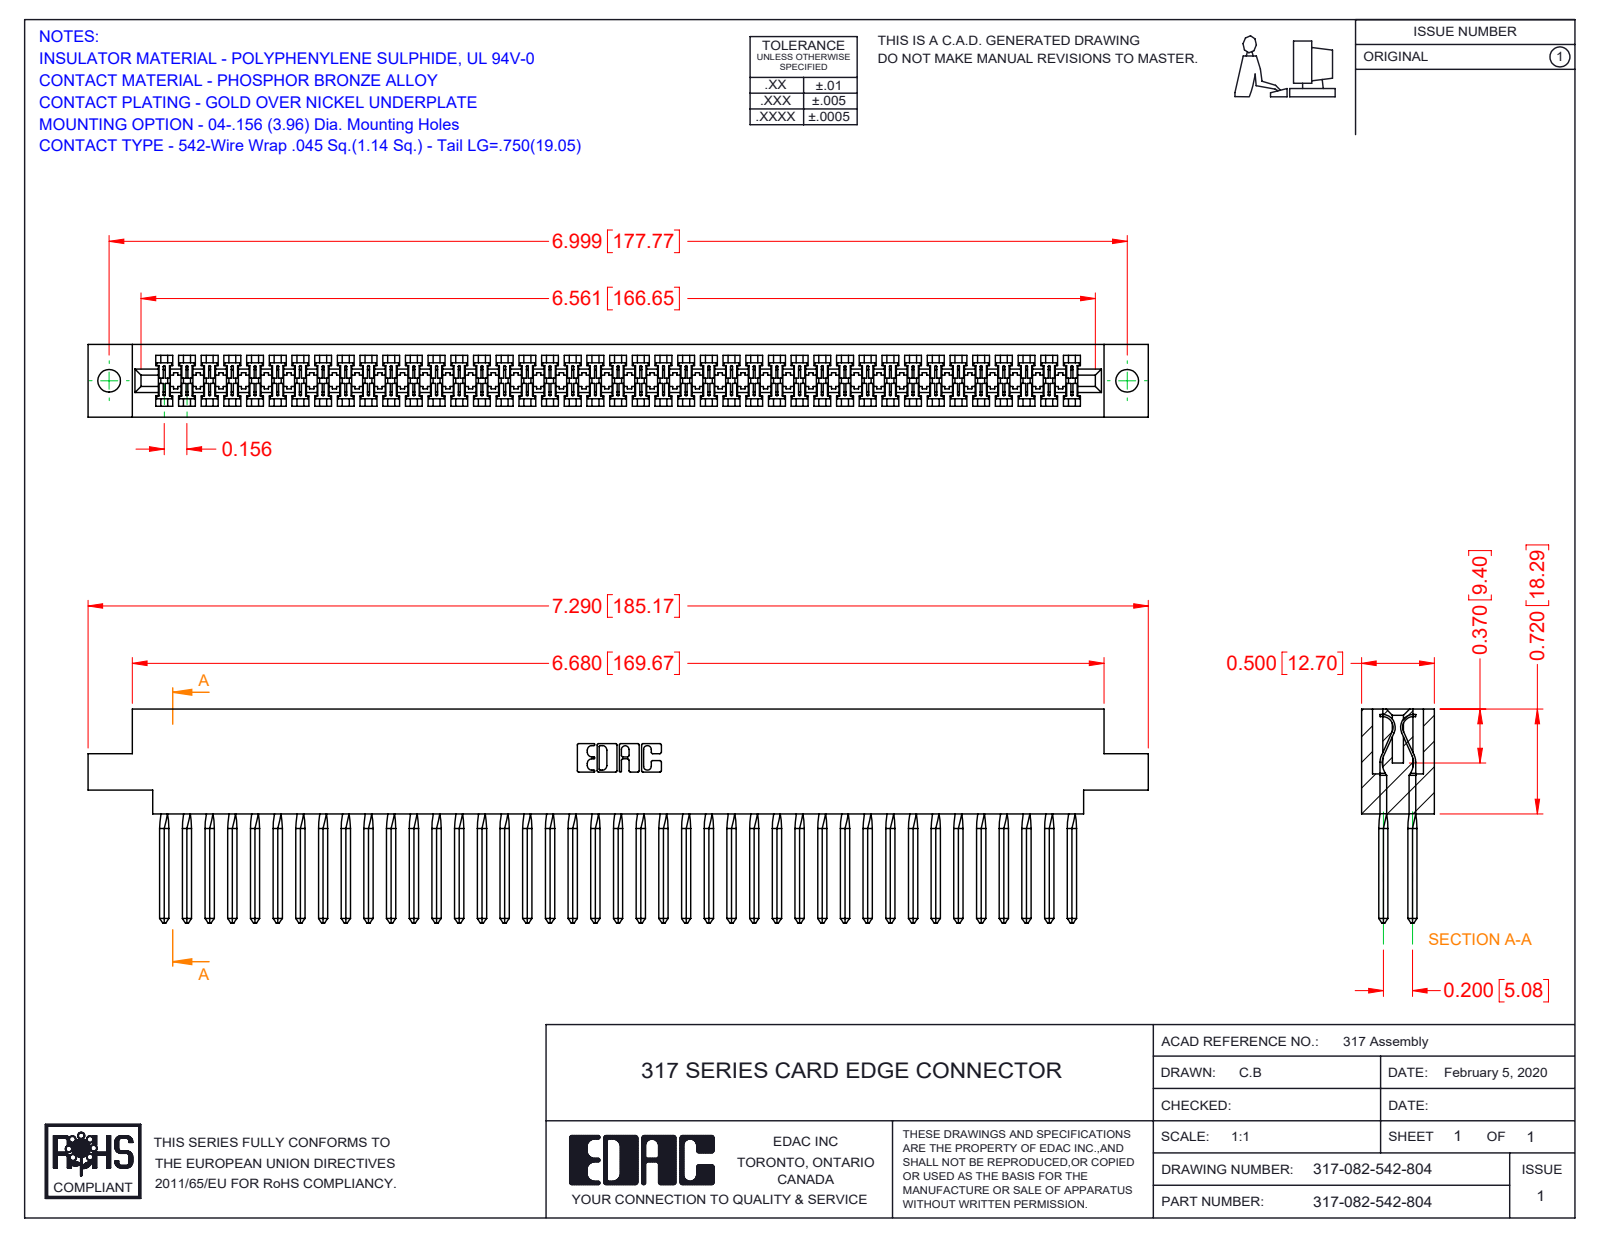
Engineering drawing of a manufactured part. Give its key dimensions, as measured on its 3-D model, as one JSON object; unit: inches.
{"part_name": "317-290-003_542; 317 Part_.156 Dia - TH; 317-082-542-804", "step_written_by": "SolidWorks 2016 (CONFIG_CONTROL_DESIGN)", "units": "inches", "bodies": {"solids": 83, "faces": 4776, "planar": 3830, "cylindrical": 618, "other": 328}, "overall_size": [7.29, 1.47, 0.5], "volume_in3": 1.843, "surface_area_in2": 64.76, "round_holes": [[0.156, 2]], "partial_cylinders_radius": [[0.006, 164], [0.01, 22], [0.007, 6], [0.031, 6], [0.026, 3], [0.074, 2], [0.089, 2], [0.1, 2]], "face_to_face_distances": [0.5, 0.075, 0.425, 0.35, 0.2, 0.046, 0.128, 0.372, 0.052, 0.297], "hole_center_spacings": [6.999]}
